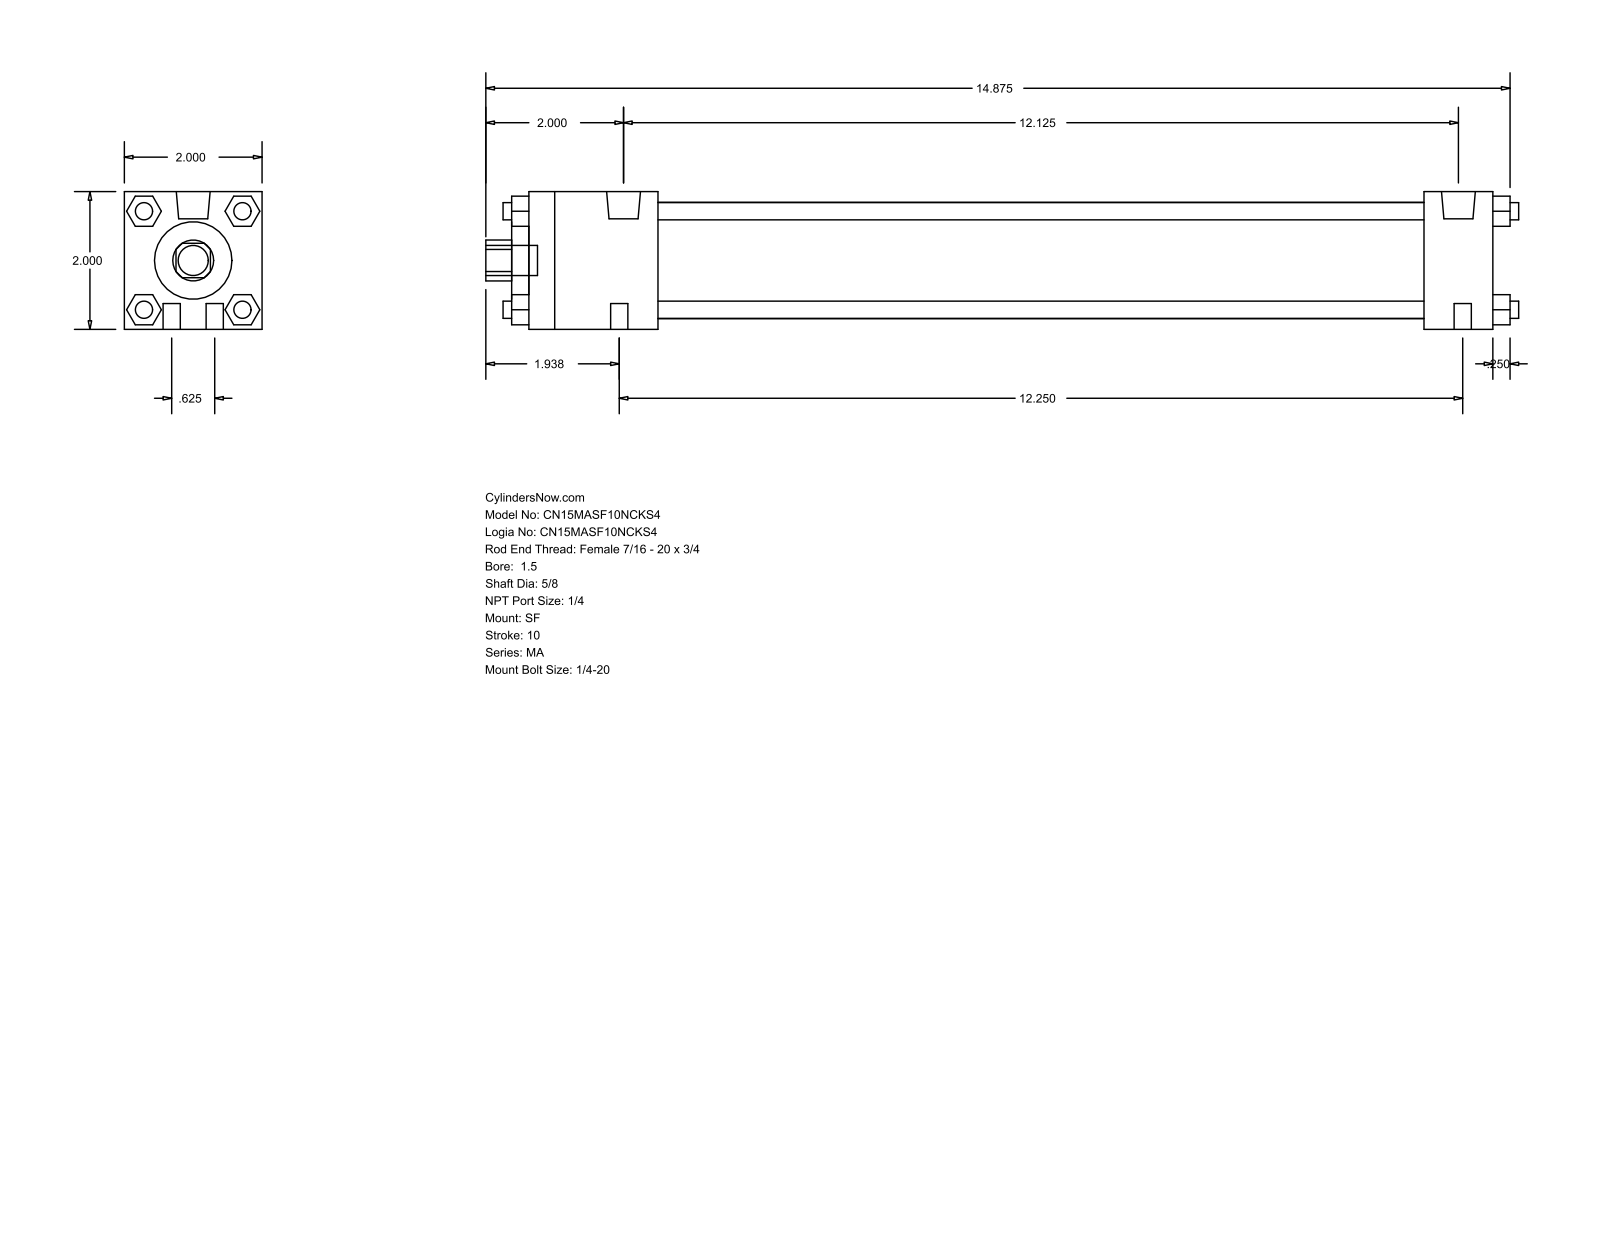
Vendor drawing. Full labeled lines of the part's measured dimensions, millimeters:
Part name (STEP PRODUCT): MA_SF__0150_0.625
STEP written by: GSSL Pune (CONFIG_CONTROL_DESIGN)
Units: millimetres
Bodies: 0 solids, 124 faces (94 planar, 30 cylindrical, 0 other)
Overall size (bounding box): 381 × 50.8 × 50.8
Round holes (diameter × count): ⌀15.88 ×1, ⌀28.57 ×1, ⌀42.93 ×1
Round bosses / shafts (diameter × count): ⌀6.35 ×8, ⌀12.49 ×2, ⌀7.94 ×2, ⌀11.11 ×1
Partial cylindrical surfaces — rounded edges, fillets, slot ends (radius × count): R7.54 ×1
Main face-to-face distances: 50.8, 355.6, 47.62, 330.19, 282.57, 307.98, 25.41, 6.35, 361.95, 53.97
